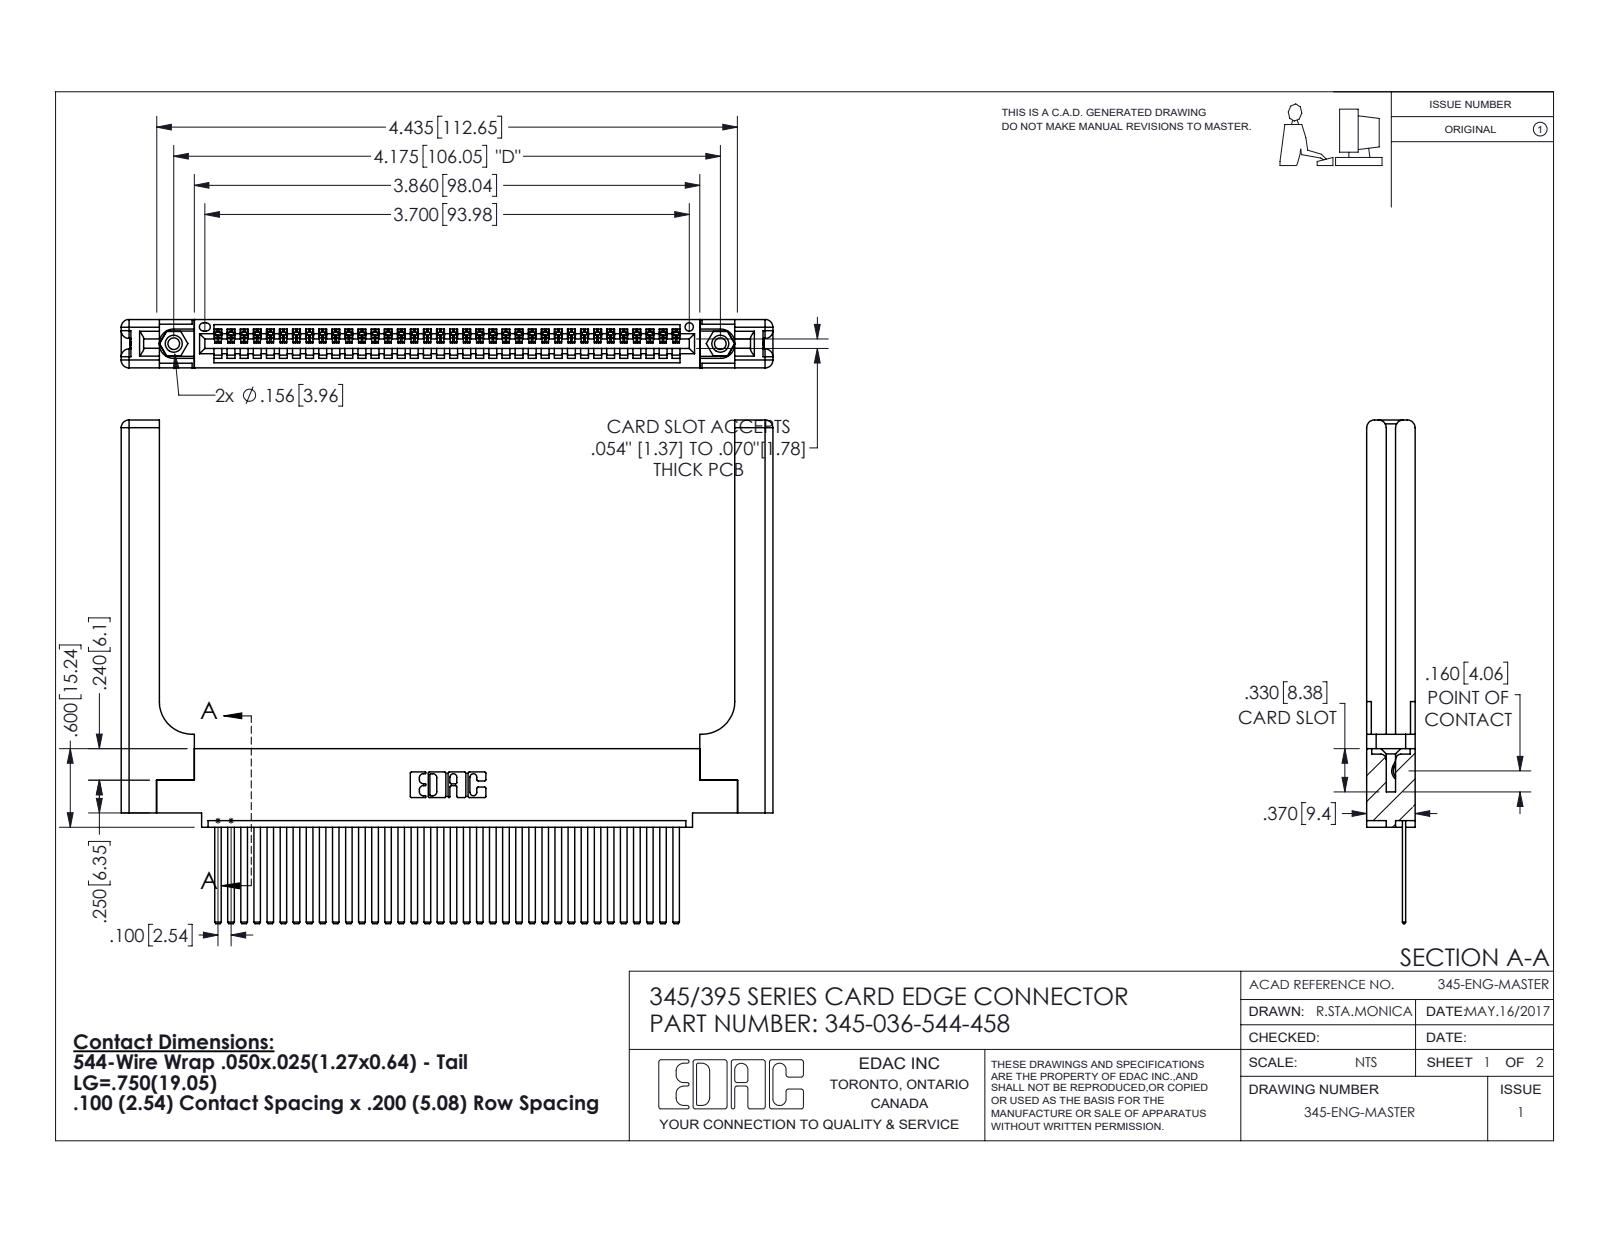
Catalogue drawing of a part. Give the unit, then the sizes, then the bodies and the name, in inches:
Units: inches
Overall size (bounding box): 4.979 × 3.847 × 0.37
Round holes (diameter × count): ⌀0.089 ×2, ⌀0.125 ×2, ⌀0.156 ×2, ⌀0.064 ×1
Round bosses / shafts (diameter × count): ⌀0.155 ×2
Partial cylindrical surfaces — rounded edges, fillets, slot ends (radius × count): R0.006 ×72, R0.01 ×22, R0.06 ×16, R0.007 ×6, R0.031 ×6, R0.026 ×3, R0.03 ×2, R0.031 ×2
Main face-to-face distances: 0.072, 0.298, 0.37, 0.098, 0.272, 0.025, 0.2, 0.148, 0.15, 0.225
Hole centre spacings: 0.27, 3.939, 4.175
Volume: 1.27 in³ · Surface area: 35.51 in²
Bodies: 41 solids, 2258 faces (1528 planar, 670 cylindrical, 60 other)
Part name (STEP PRODUCT): 345-292-001_345-293-144; 345 Part_0.110 Offset - 0.156 Dia-TH; 345-220-058_345-220-058; 345-036-544-458 (+1 more)
STEP written by: SolidWorks 2016 (CONFIG_CONTROL_DESIGN)
